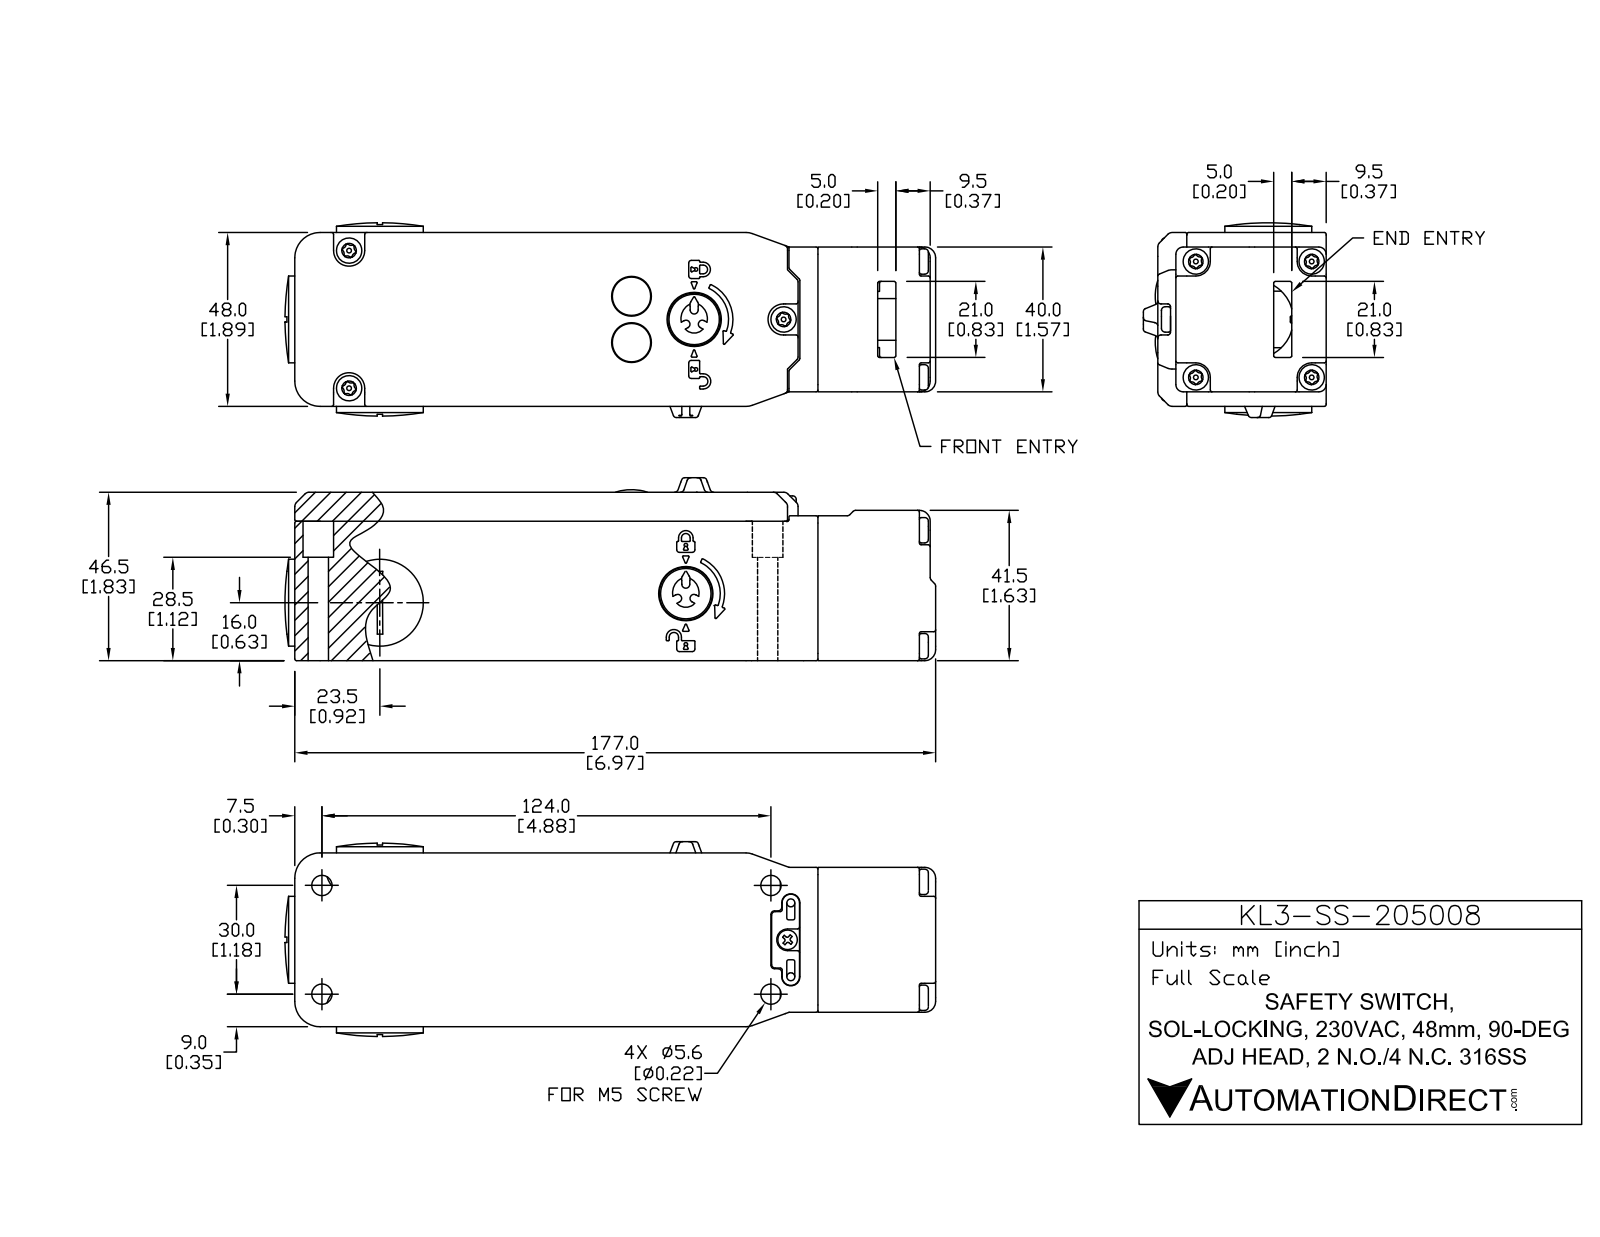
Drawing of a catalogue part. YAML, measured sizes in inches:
part_name: "KL3-SS-205008"
step_written_by: "SolidWorks 2017 (AUTOMOTIVE_DESIGN)"
units: inches
bodies: {solids: 19, faces: 3255, planar: 757, cylindrical: 1350, other: 1148}
overall_size: [7.075, 2.118, 1.988]
volume: 8.074
surface_area: 141.5
round_holes:
  - {diameter: 0.157, count: 7}
  - {diameter: 0.118, count: 6}
  - {diameter: 0.165, count: 4}
  - {diameter: 0.197, count: 4}
  - {diameter: 0.22, count: 4}
  - {diameter: 0.354, count: 4}
  - {diameter: 0.177, count: 3}
  - {diameter: 0.087, count: 2}
  - {diameter: 0.142, count: 2}
  - {diameter: 0.268, count: 2}
  - {diameter: 0.319, count: 2}
  - {diameter: 0.358, count: 2}
round_bosses_or_shafts:
  - {diameter: 0.276, count: 7}
  - {diameter: 0.138, count: 7}
  - {diameter: 0.051, count: 7}
  - {diameter: 0.039, count: 4}
  - {diameter: 0.236, count: 3}
  - {diameter: 0.945, count: 2}
  - {diameter: 0.709, count: 2}
  - {diameter: 0.449, count: 2}
partial_cylinders:
  - {radius: 0.02, count: 405}
  - {radius: 0.008, count: 119}
  - {radius: 0.039, count: 105}
  - {radius: 0.012, count: 41}
  - {radius: 0.016, count: 29}
  - {radius: 0.059, count: 25}
  - {radius: 0.031, count: 20}
  - {radius: 0.006, count: 14}
face_to_face_distances: [0.13, 0.087, 1.76, 1.831, 1.89, 1.516, 1.744, 1.654, 0.157, 1.602]
hole_center_spacings: [0.891, 1.26, 1.339, 0.165, 0.181, 0.262, 0.275, 0.287]
